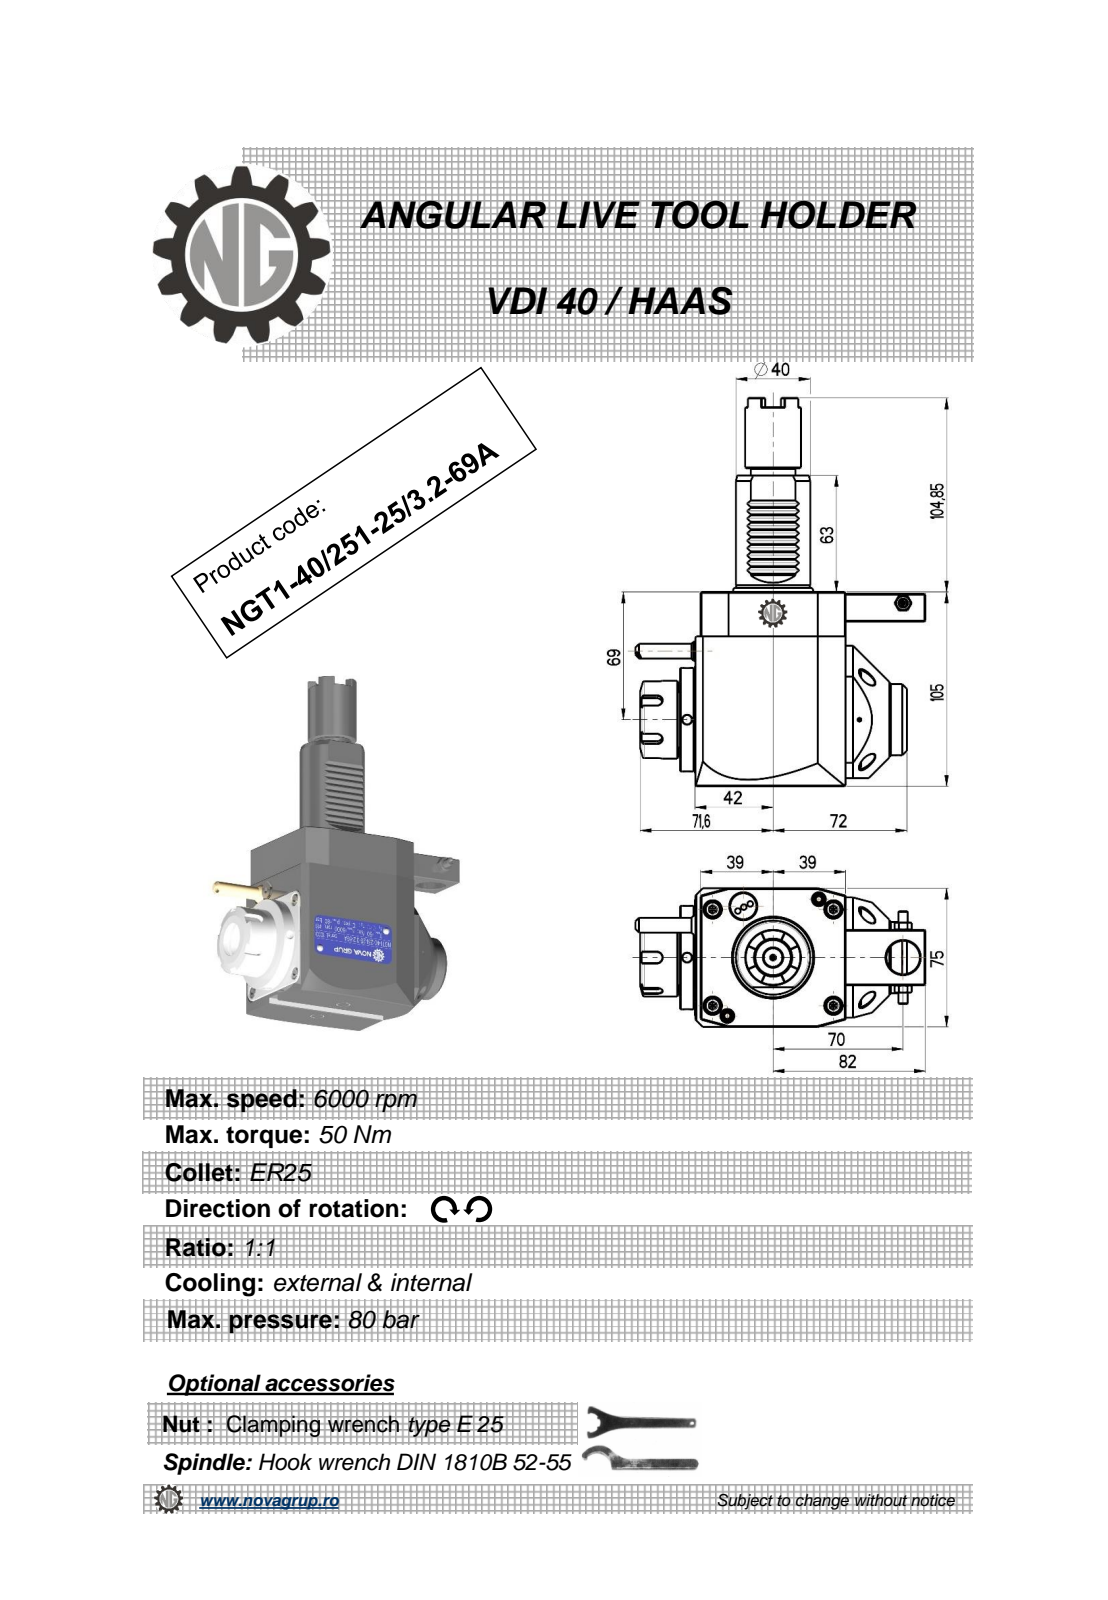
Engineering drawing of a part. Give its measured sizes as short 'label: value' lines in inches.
name: NGT1_40_251_25_3_2_69A
written by: PRO/ENGINEER BY PARAMETRIC TECHNOLOGY CORPORATION, 2010280 (CONFIG_CONTROL_DESIGN)
unit: in
bodies: 1 solid, 465 faces (216 planar, 91 cylindrical, 158 other)
size: 8.262 × 6.147 × 2.953
volume: 52.65 in³; area: 115.2 in²
holes: 3× ⌀0.197, 1× ⌀0.118, 1× ⌀0.165, 1× ⌀0.374, 1× ⌀0.709, 1× ⌀0.799
bosses: 1× ⌀2.205, 1× ⌀1.693, 1× ⌀1.654, 1× ⌀1.575, 1× ⌀1.516, 1× ⌀1.299, 1× ⌀1.181, 1× ⌀0.945
rounds: 12× R0.01, 10× R0.012, 6× R0.008, 5× R0.118, 1× R0.02, 1× R0.394, 1× R1.575
face distances: 2.953, 4.134, 3.504, 3.189, 0.315, 0.433, 0.039, 0.118, 0.11, 3.071
hole spacings: 1.185, 1.611, 2.421, 4.577, 5.206
